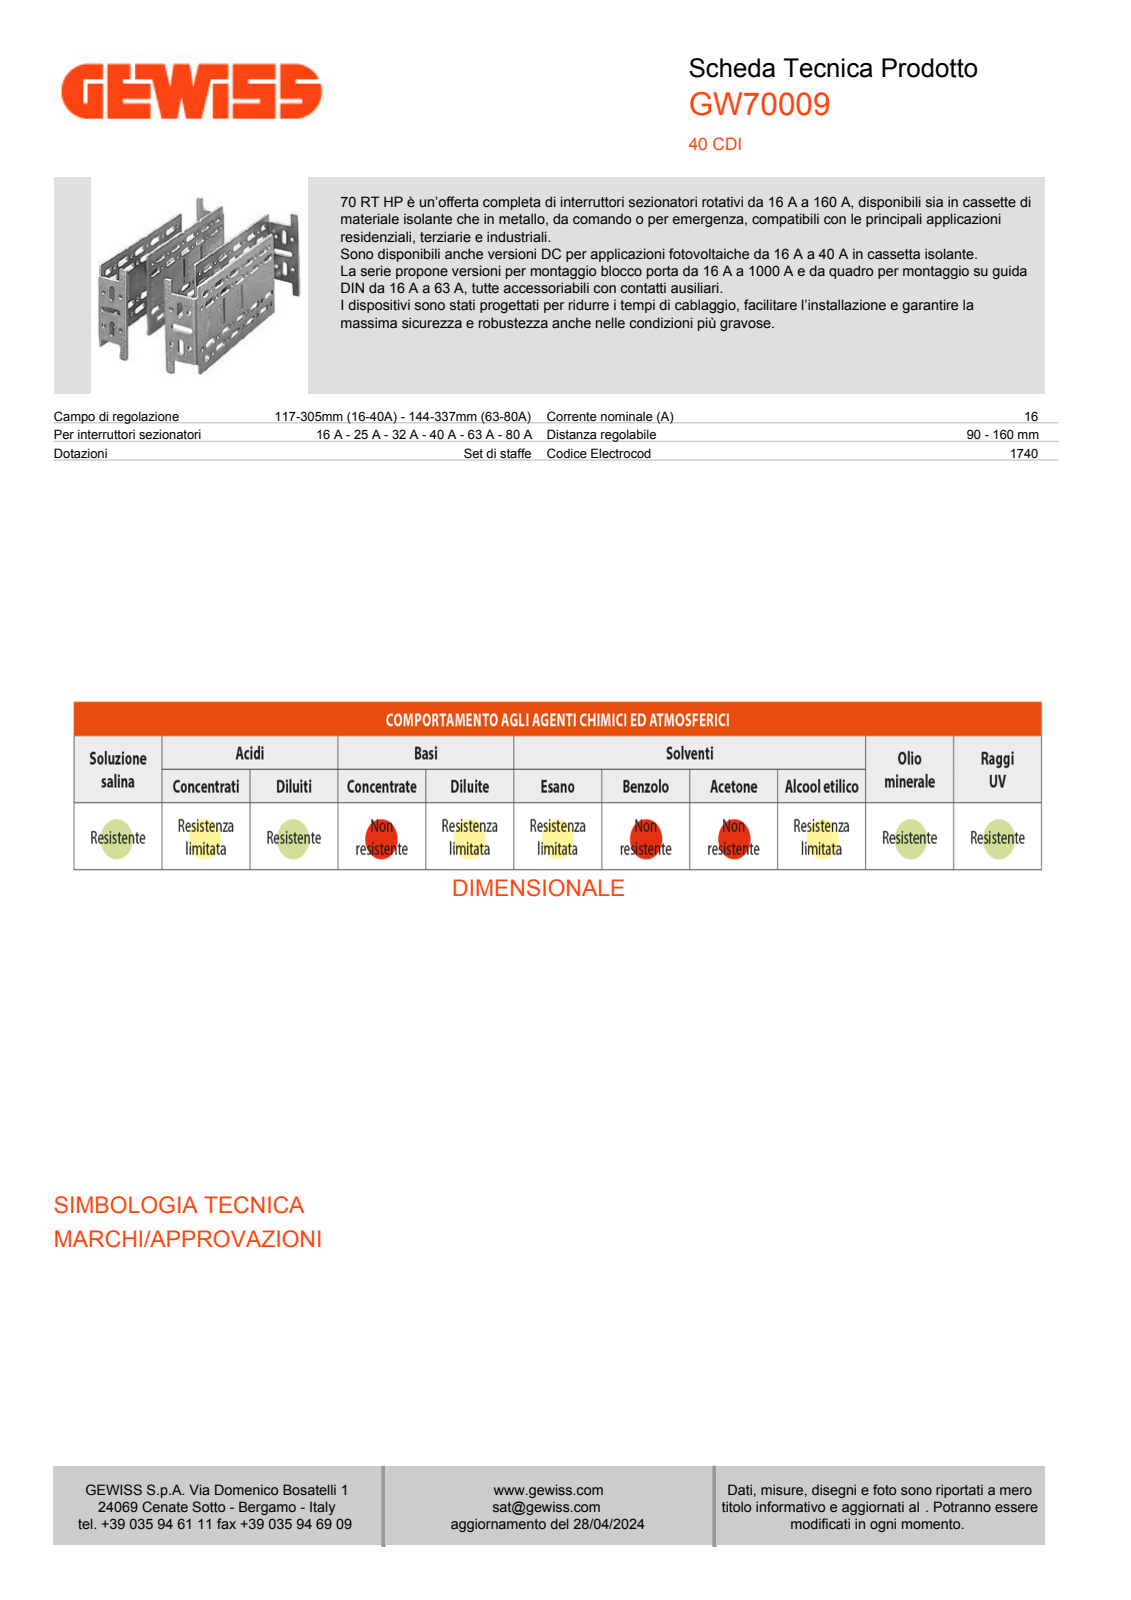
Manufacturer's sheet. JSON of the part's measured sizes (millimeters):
{"part_name": "GW70009", "step_written_by": "CREO PARAMETRIC BY PTC INC, 2020354 (CONFIG_CONTROL_DESIGN)", "units": "millimeters", "bodies": {"solids": 1, "faces": 178, "planar": 82, "cylindrical": 96, "other": 0}, "overall_size": [87, 48.5, 20], "volume_mm3": 5574, "surface_area_mm2": 9113, "round_holes": [[2.6, 24]], "partial_cylinders_radius": [[1.6, 46], [0.5, 1], [2, 1]], "face_to_face_distances": [1.5, 3.2, 6, 27, 45, 20, 13.6, 31.4, 10.4, 34.6], "hole_center_spacings": [16.6, 33.2, 12.27, 29.04, 8.41, 26.77, 27.64, 27.95]}
